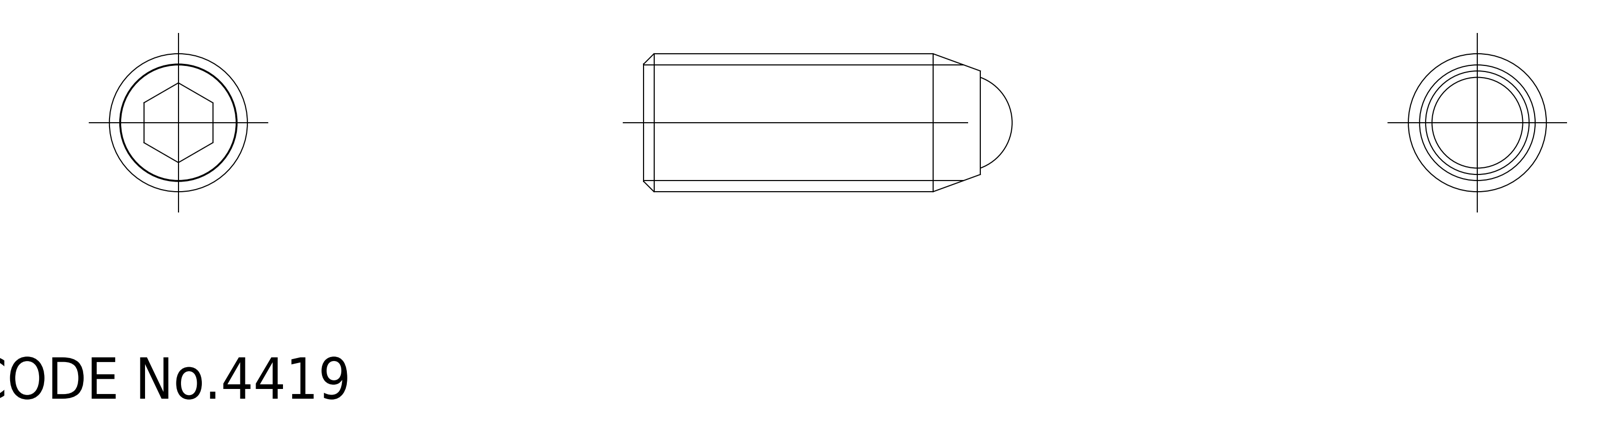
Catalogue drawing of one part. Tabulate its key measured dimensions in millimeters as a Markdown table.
| quantity | value |
| --- | --- |
| part name | ball; SCSS_M10_25_R_18126_36 |
| STEP written by | CADfix (AUTOMOTIVE_DESIGN) |
| units | millimeters |
| bodies | 2 solids, 20 faces (0 planar, 0 cylindrical, 20 other) |
| overall size | 26.7 × 10 × 10 |
| volume | 1 685 mm³ |
| surface area | 1 252 mm² |
